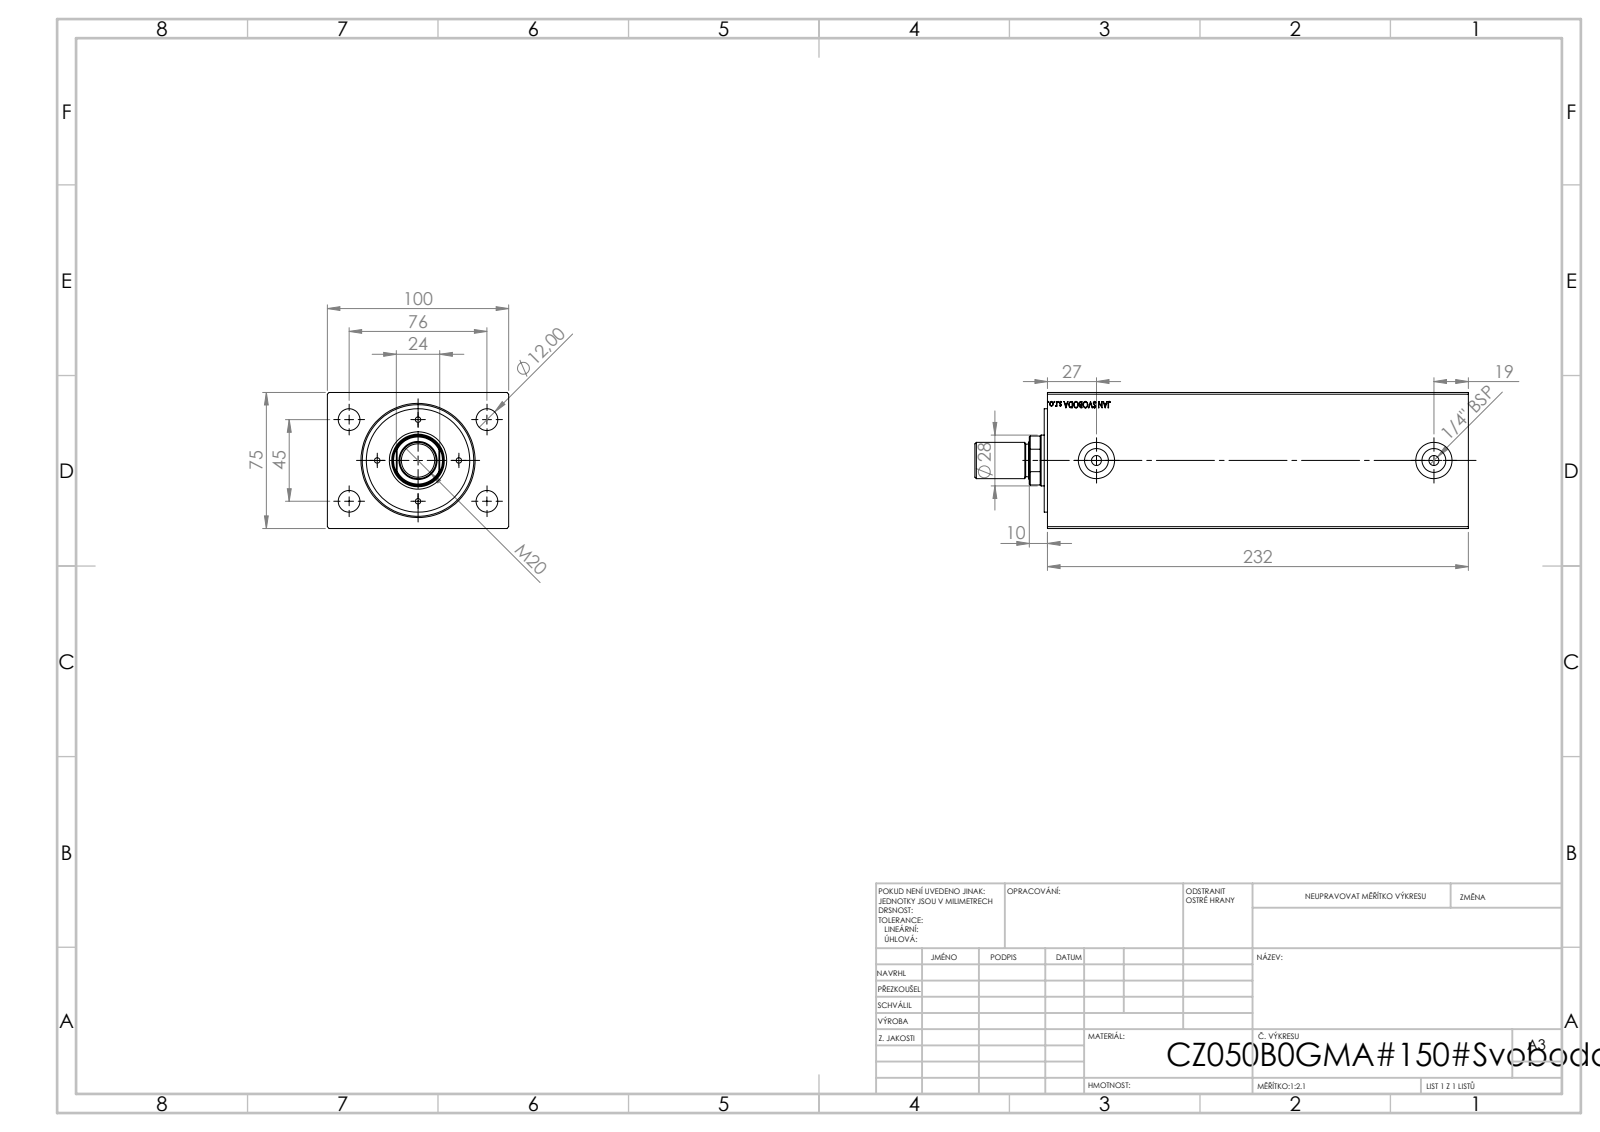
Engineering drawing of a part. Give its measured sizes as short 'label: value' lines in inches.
name: V500CZ; V500CZ_B_VC; V500CZ_MALE_METRIC
written by: SolidWorks 2019 (CONFIG_CONTROL_DESIGN)
unit: in
bodies: 4 solids, 888 faces (404 planar, 62 cylindrical, 422 other)
size: 10.709 × 3.937 × 2.953
volume: 92.51 in³; area: 275.4 in²
holes: 4× ⌀0.118, 4× ⌀0.472, 2× ⌀0.217, 2× ⌀0.518, 2× ⌀0.787, 1× ⌀0.728, 1× ⌀1.102, 1× ⌀1.142, 1× ⌀1.417, 1× ⌀1.969, 1× ⌀2.421
bosses: 1× ⌀2.244, 1× ⌀0.787, 1× ⌀0.709
rounds: 1× R0.531
face distances: 2.953, 3.937, 9.134, 8.433, 0.701, 0.394, 0.323, 0.071, 8.11, 8.811
hole spacings: 0.886, 1.076, 1.253, 1.496, 1.739, 1.772, 2.319, 2.541
